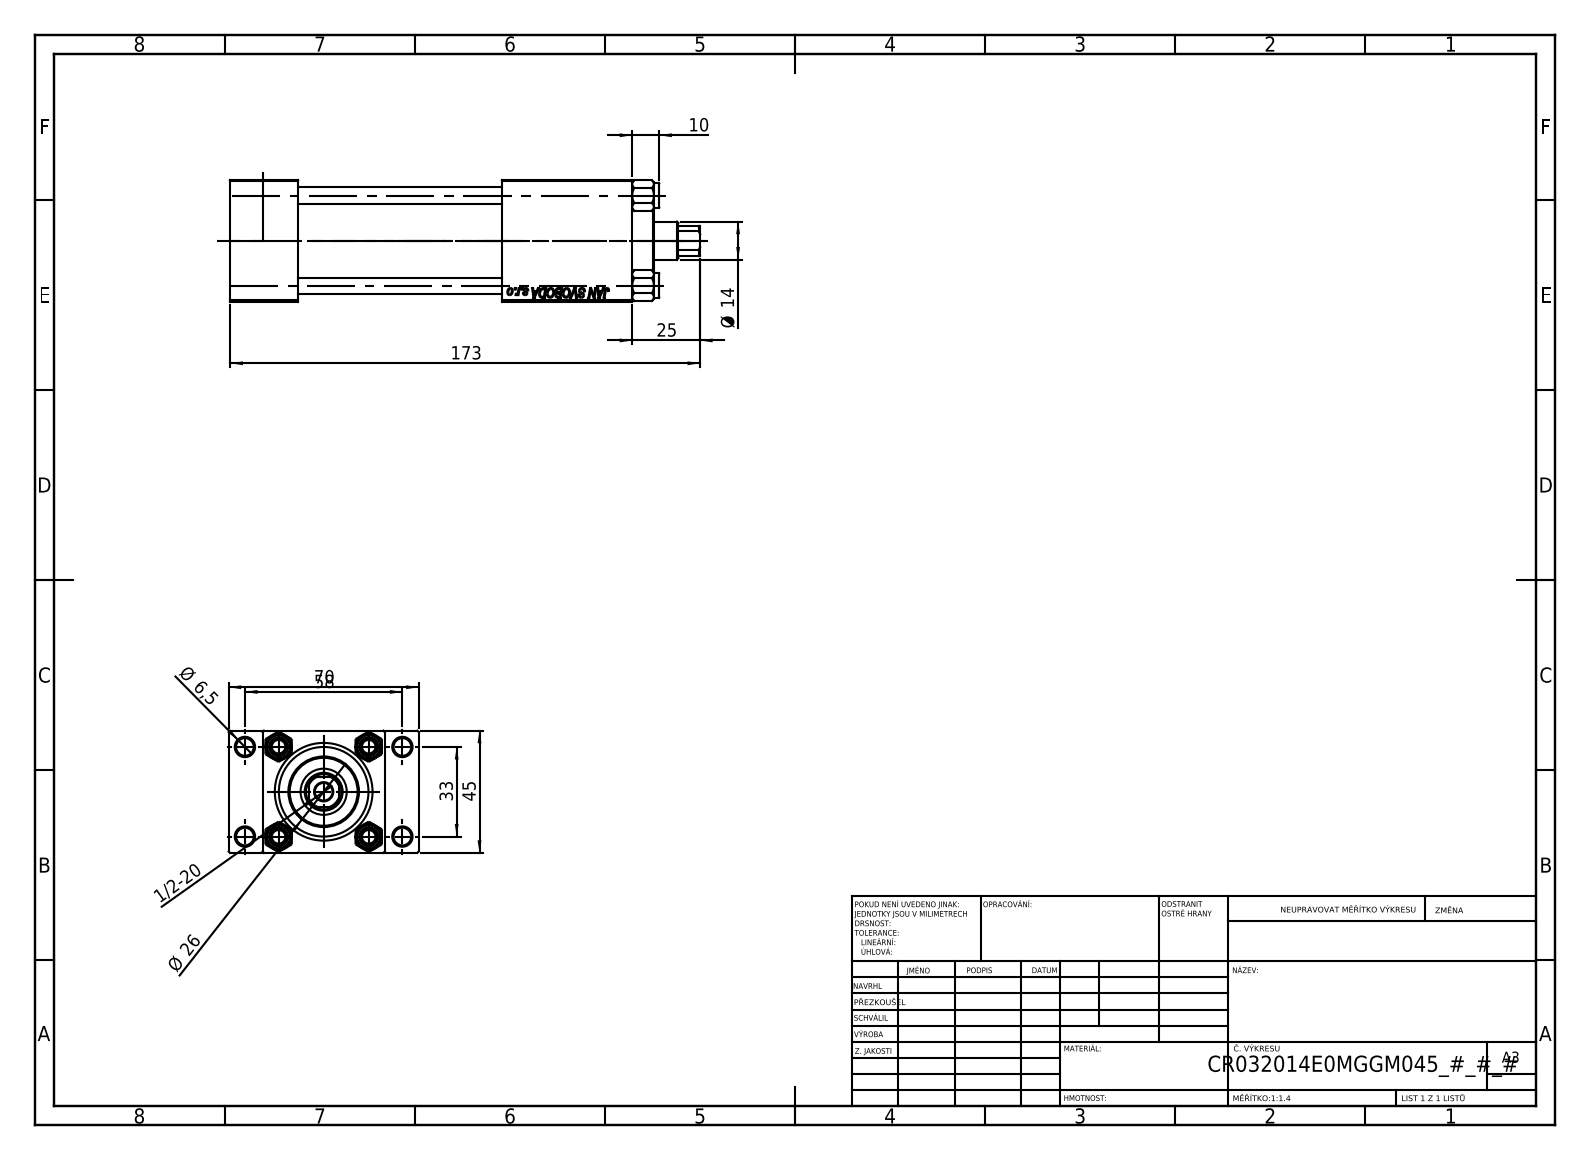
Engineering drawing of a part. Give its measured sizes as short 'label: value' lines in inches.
name: V215CR_TYCINKA_E; V215CR_E_Body; NUT_M5_E; V215_VC_A (+1 more)
written by: SolidWorks 2019 (CONFIG_CONTROL_DESIGN)
unit: in
bodies: 11 solids, 1136 faces (497 planar, 87 cylindrical, 552 other)
size: 6.811 × 2.756 × 1.772
volume: 14.34 in³; area: 131.1 in²
holes: 5× ⌀0.256, 4× ⌀0.236, 2× ⌀0.276, 2× ⌀0.518, 2× ⌀0.787, 1× ⌀0.551, 1× ⌀0.669, 1× ⌀0.945, 1× ⌀1.26, 1× ⌀1.299
bosses: 4× ⌀0.354, 1× ⌀1.496, 1× ⌀1.024
rounds: 1× R0.256
face distances: 1.772, 0.984, 0.492, 2.264, 5.827, 4.843, 2.756, 3.937, 2.953, 1.89
hole spacings: 0.488, 0.924, 1.307, 1.314, 1.392, 1.795, 2.219, 1.299
